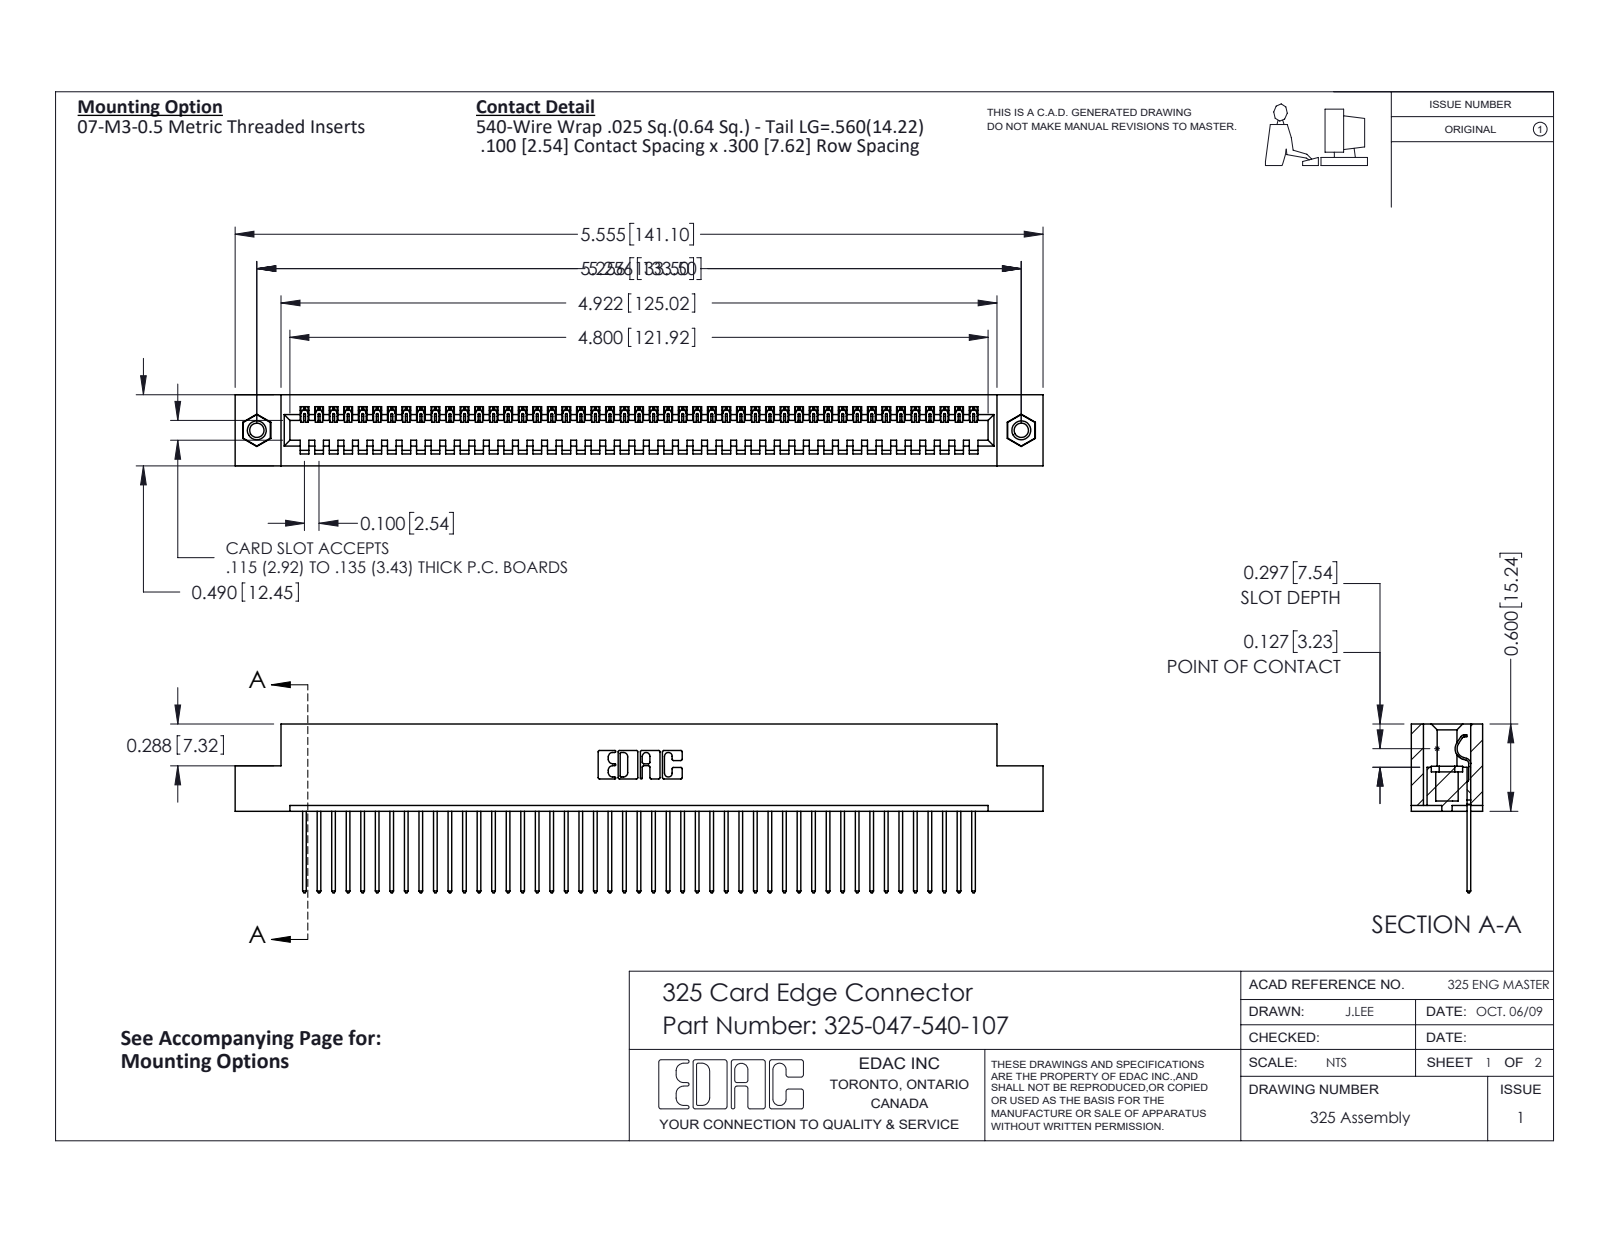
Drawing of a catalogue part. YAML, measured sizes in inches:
part_name: "325 Part_TI; 345-250-001_345-250-005-103; 325-292-001_325-293-140; 325-047-540-107"
step_written_by: "SolidWorks 2016 (CONFIG_CONTROL_DESIGN)"
units: inches
bodies: {solids: 50, faces: 2900, planar: 2076, cylindrical: 808, other: 16}
overall_size: [5.555, 1.16, 0.49]
volume: 1.099
surface_area: 31.39
round_holes:
  - {diameter: 0.098, count: 2}
  - {diameter: 0.125, count: 2}
  - {diameter: 0.16, count: 2}
round_bosses_or_shafts:
  - {diameter: 0.155, count: 2}
partial_cylinders:
  - {radius: 0.006, count: 94}
  - {radius: 0.01, count: 94}
  - {radius: 0.01, count: 22}
  - {radius: 0.007, count: 6}
  - {radius: 0.031, count: 6}
  - {radius: 0.026, count: 3}
  - {radius: 0.014, count: 1}
  - {radius: 0.022, count: 1}
face_to_face_distances: [0.083, 0.407, 0.49, 0.3, 0.107, 0.383, 0.025, 0.325, 0.56, 0.263]
hole_center_spacings: [5.256]
